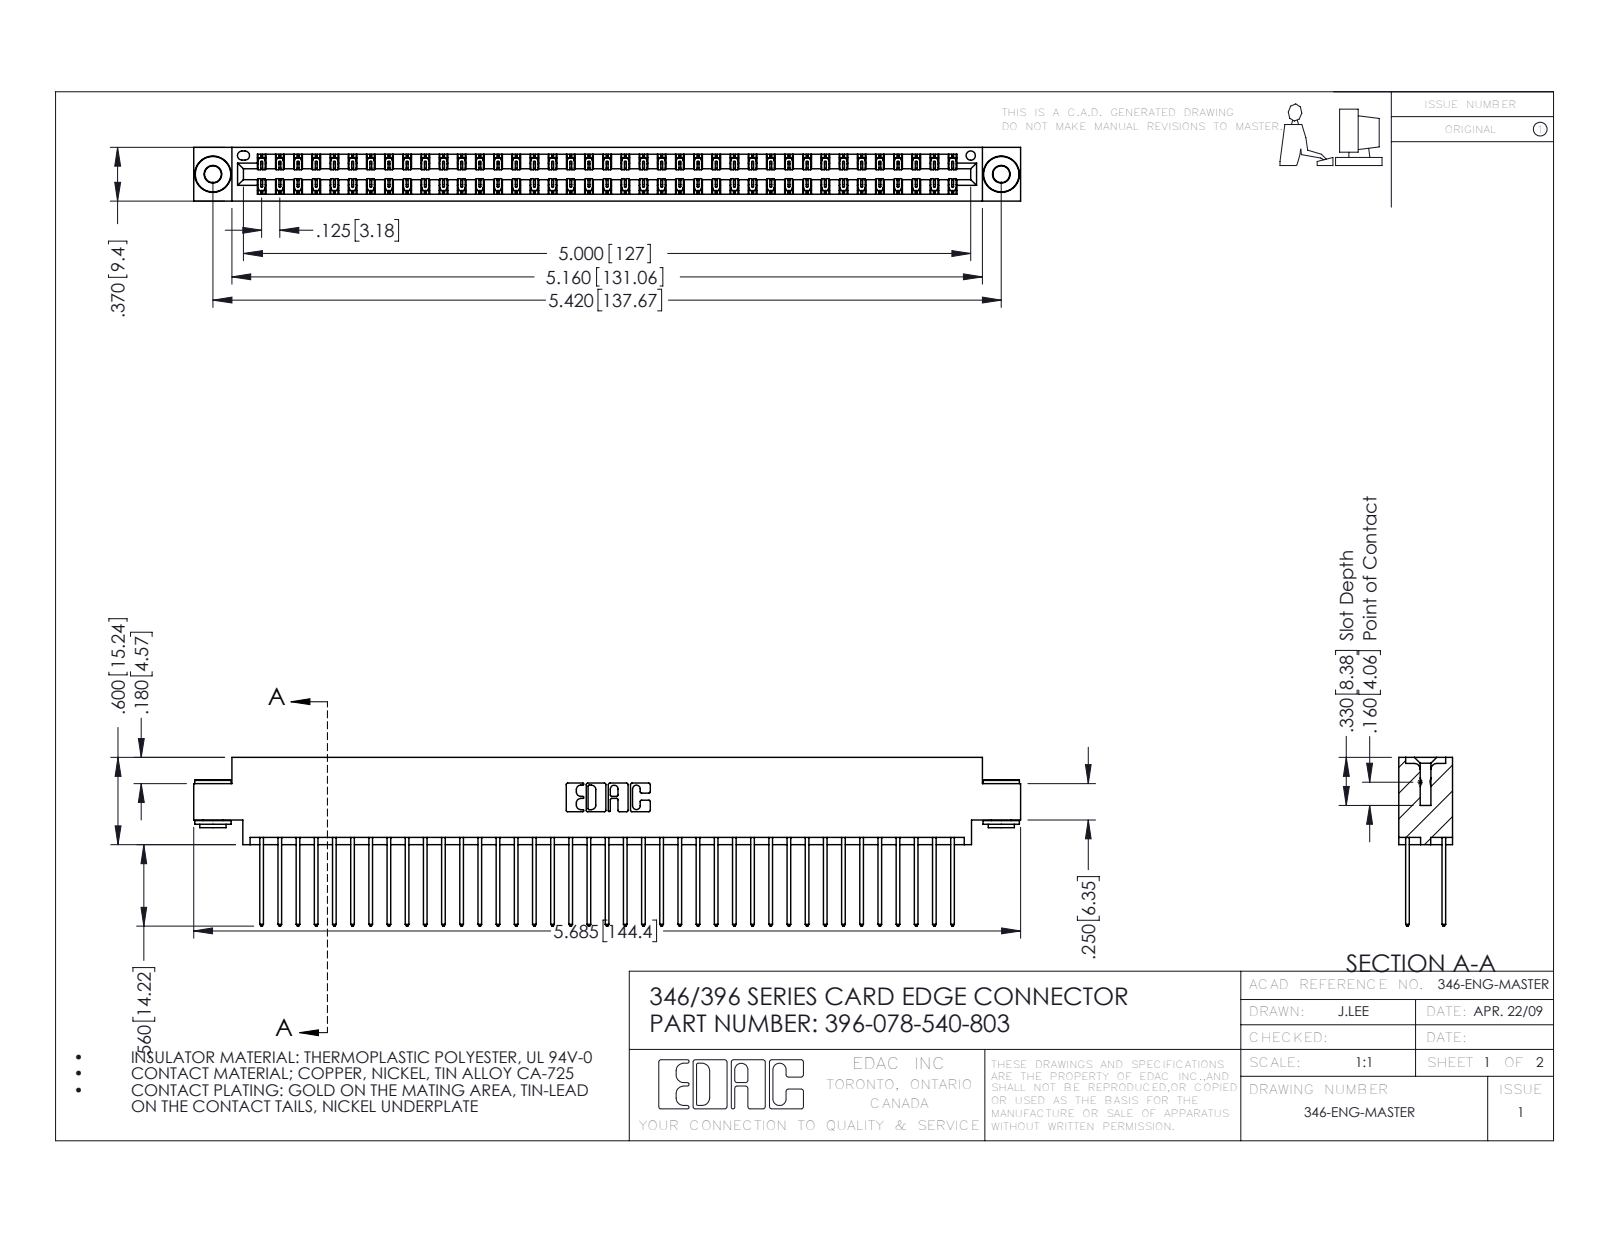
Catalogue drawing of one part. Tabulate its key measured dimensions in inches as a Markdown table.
| quantity | value |
| --- | --- |
| part name | 345-292-001_345-293-140; 345-250-002_345-250-002-102; 346 Part_0.170 Offset - 0.156 Dia-TH; 396-078-540-803 |
| STEP written by | SolidWorks 2016 (CONFIG_CONTROL_DESIGN) |
| units | inches |
| bodies | 81 solids, 4220 faces (2820 planar, 1392 cylindrical, 8 other) |
| overall size | 5.685 × 1.16 × 0.37 |
| volume | 0.868 in³ |
| surface area | 33 in² |
| round holes (diameter × count) | 0.116 × 2, 0.156 × 2, 0.064 × 1 |
| round bosses / shafts (diameter × count) | 0.25 × 2, 0.18 × 2, 0.136 × 2 |
| partial cylindrical surfaces (radius × count) | 0.006 × 117, 0.01 × 78, 0.01 × 22, 0.007 × 6, 0.031 × 6, 0.026 × 3, 0.014 × 2, 0.022 × 2 |
| main face-to-face distances | 0.048, 0.322, 0.25, 0.025, 0.37, 0.072, 0.298, 0.275, 0.148, 0.222 |
| hole center spacings | 0.246, 5.211, 5.42 |
